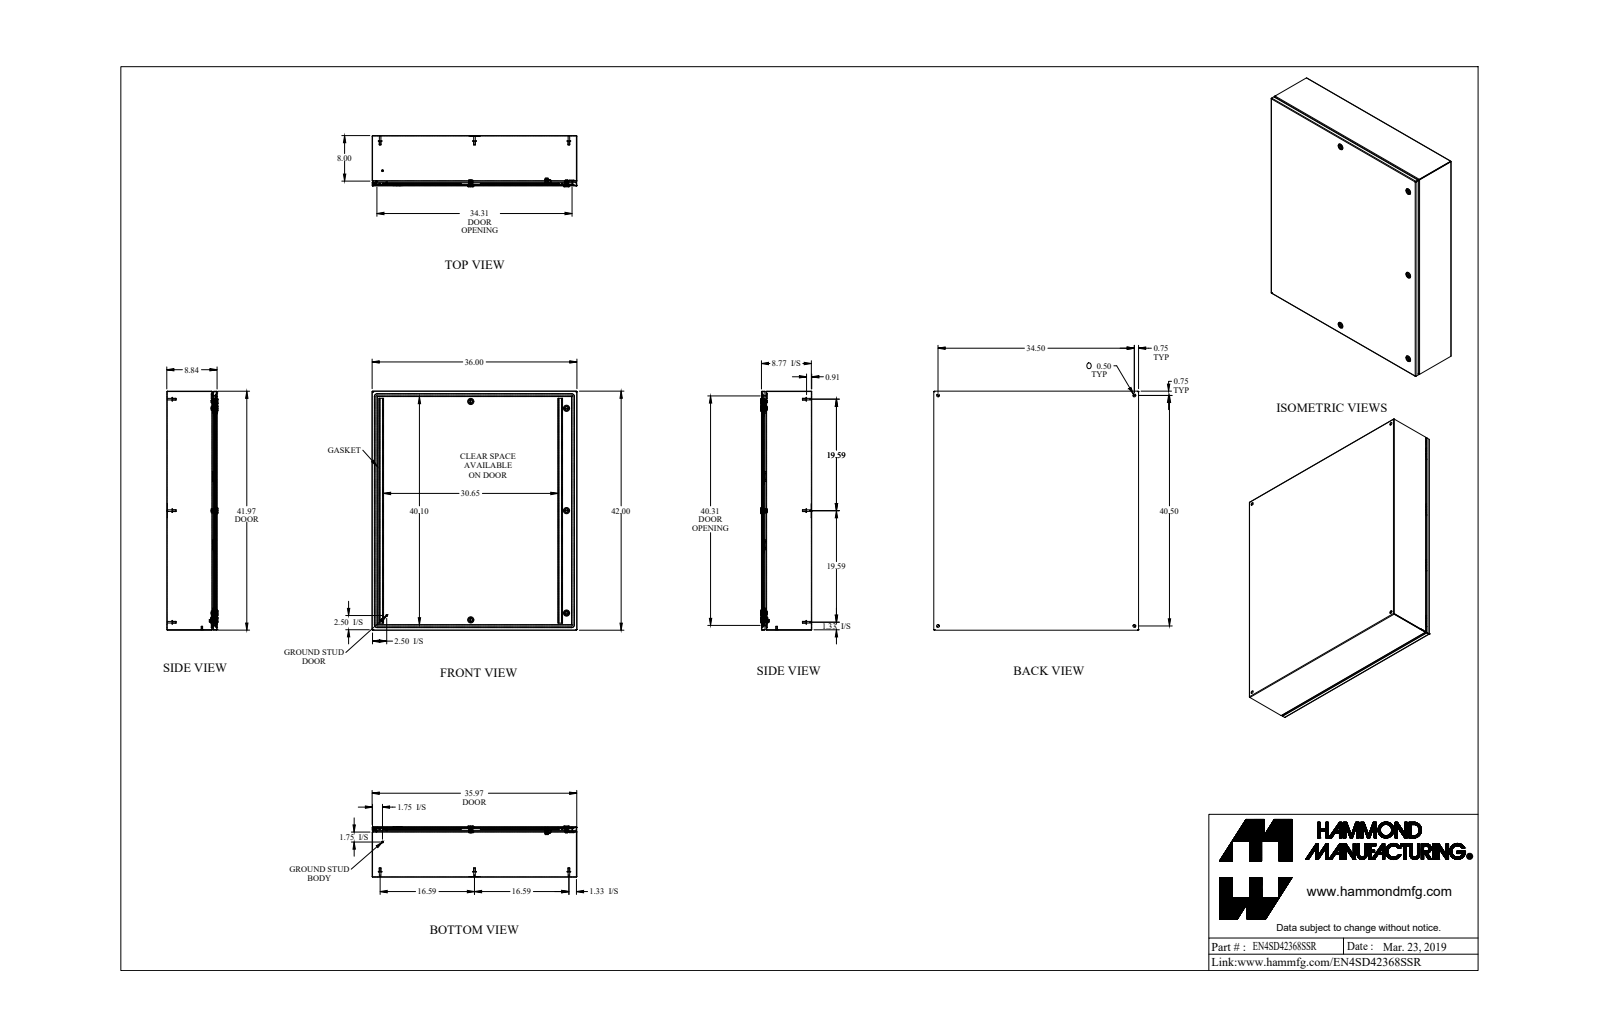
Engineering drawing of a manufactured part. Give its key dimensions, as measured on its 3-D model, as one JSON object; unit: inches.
{"part_name": "EN4SD42368SSR_Default", "step_written_by": "SolidWorks 2019 (CONFIG_CONTROL_DESIGN)", "units": "inches", "bodies": {"solids": 64, "faces": 1731, "planar": 896, "cylindrical": 550, "other": 285}, "overall_size": [42, 36, 9.002], "volume_in3": 358.8, "surface_area_in2": 10118, "round_holes": [[0.5, 9], [0.197, 5], [0.387, 5], [0.63, 5], [0.768, 5], [0.172, 1], [0.196, 1], [0.24, 1], [0.242, 1], [0.275, 1], [0.375, 1]], "round_bosses_or_shafts": [[0.313, 10], [0.625, 9], [0.275, 8], [1.1, 5], [0.785, 5], [0.625, 5], [0.525, 5], [0.236, 5]], "partial_cylinders_radius": [[0.01, 24], [0.048, 24], [0.036, 20], [0.108, 20], [0.062, 18], [0.094, 10], [0.125, 10], [0.016, 9]], "face_to_face_distances": [0.072, 8.77, 8.698, 8.842, 35.928, 41.928, 35.856, 36, 41.856, 42], "hole_center_spacings": [2.507, 16.622, 16.881, 17.943, 17.985, 20.278, 25.529, 33.504]}
